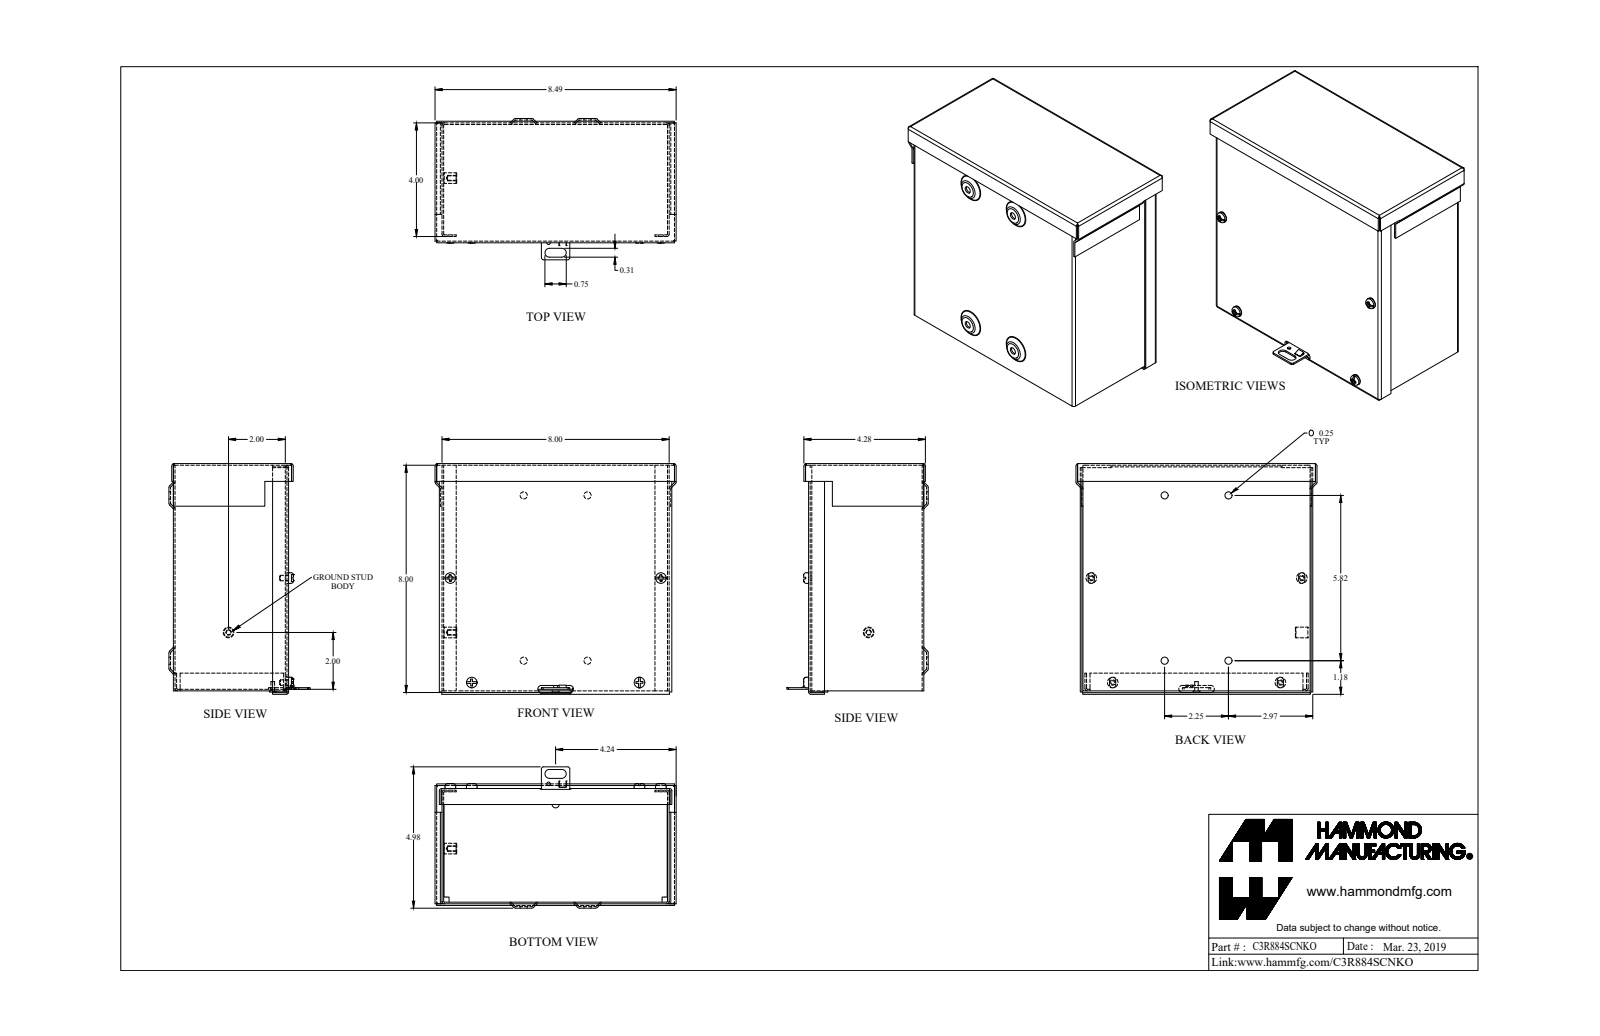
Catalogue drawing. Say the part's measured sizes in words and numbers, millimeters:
The part is named "C3R884SCNKO_Default". Its 3-D file was written by "SolidWorks 2019 (CONFIG_CONTROL_DESIGN)". It is 11 solids with 404 faces: 211 planar, 107 cylindrical and 86 other. Overall it measures 215.6 by 206.2 by 126.4 millimeters. Its volume is 292 500 cubic millimeters and its surface area 409 500 square millimeters. Round holes: 4 of diameter 4.3, 4 of diameter 6.4, 1 of diameter 3.2, 1 of diameter 3.5, 1 of diameter 4. Round bosses or shafts: 4 of diameter 9.5, 4 of diameter 4.8, 1 of diameter 9.5, 1 of diameter 3.2. Partial cylindrical surfaces (rounded edges, fillets, slot ends): 21 of radius 0.7, 21 of radius 2.2, 8 of radius 2.8, 8 of radius 3.2, 2 of radius 4. The main face-to-face distances are 1.4, 101.6, 201.8, 100.2, 103, 203.2, 1.4, 200.3, 200.3, 201.8. The hole center spacings are 98.8, 143.3, 50.4, 57.2, 95.4, 105.4, 147.8, 158.4.
